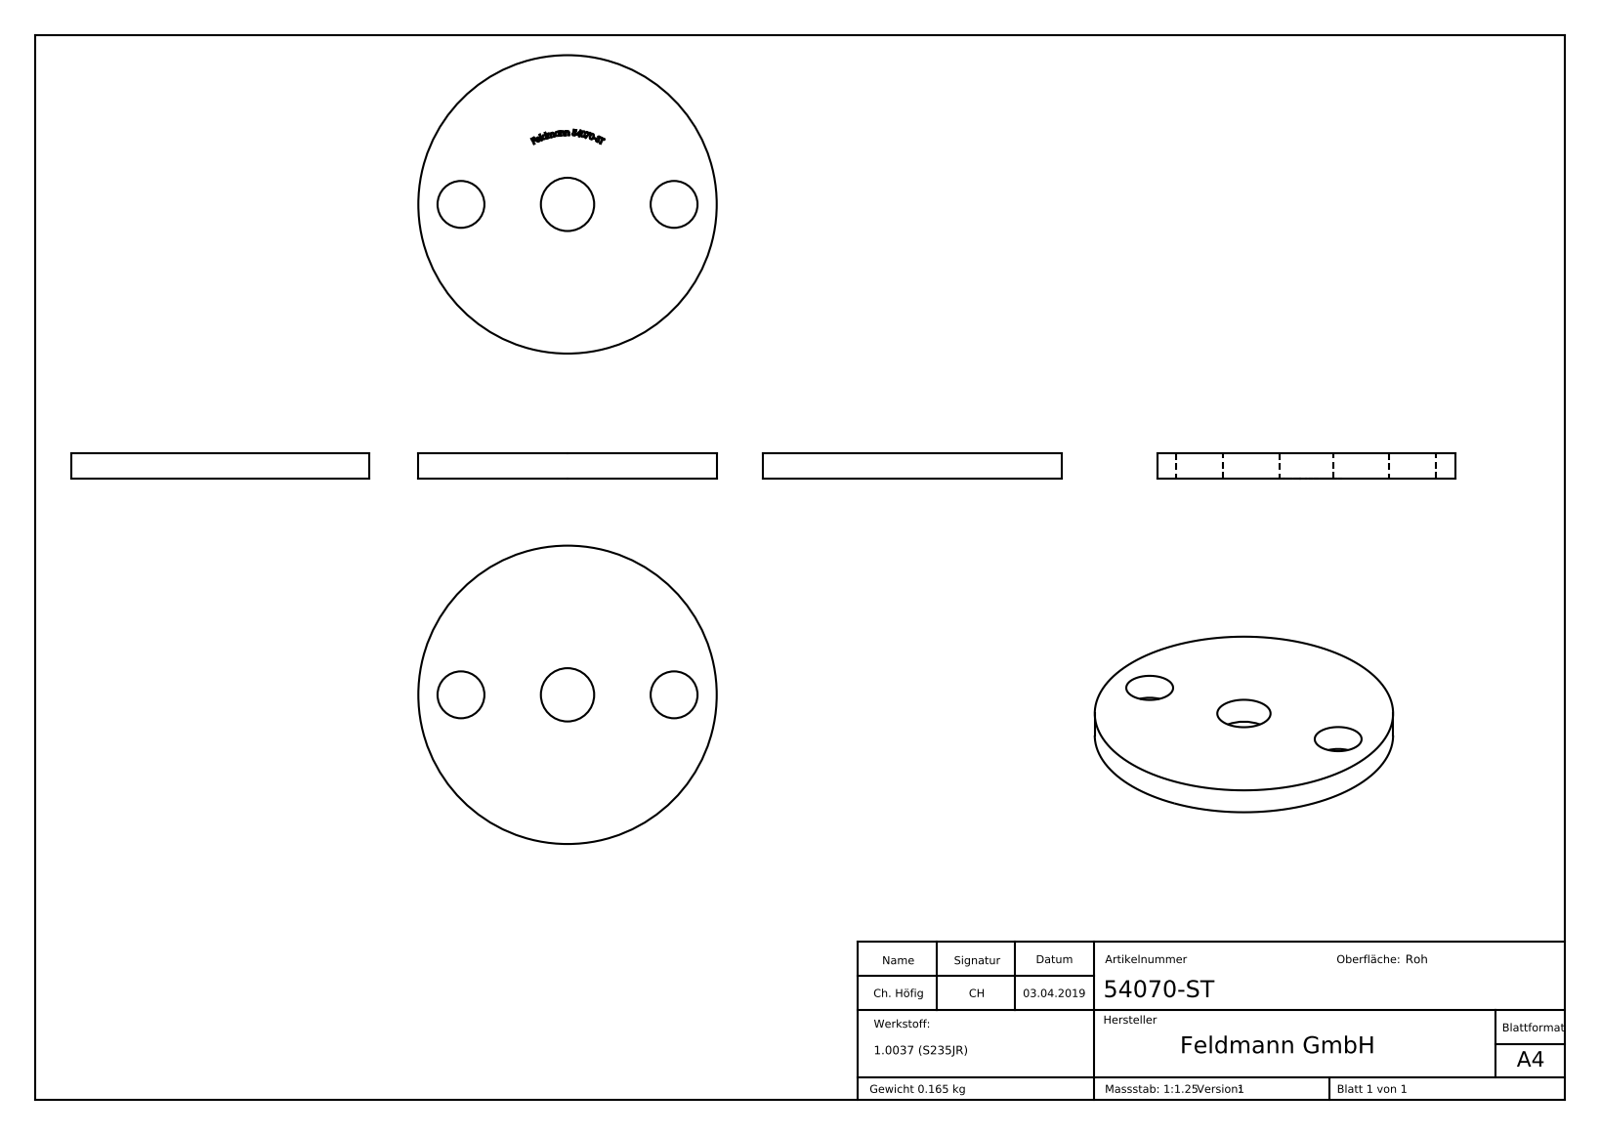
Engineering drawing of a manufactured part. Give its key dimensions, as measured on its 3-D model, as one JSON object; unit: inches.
{"part_name": "54070-ST", "step_written_by": "SolidWorks 2015 (CONFIG_CONTROL_DESIGN)", "units": "inches", "bodies": {"solids": 1, "faces": 214, "planar": 117, "cylindrical": 8, "other": 89}, "overall_size": [2.756, 2.756, 0.236], "volume_in3": 1.294, "surface_area_in2": 14.03, "round_holes": [[0.433, 2], [0.492, 1]], "round_bosses_or_shafts": [[2.756, 1]], "face_to_face_distances": [0.236, 0.232, 0.021, 0.026, 0.026, 0.033, 0.028, 0.031, 0.052, 0.029], "hole_center_spacings": [0.984, 1.969]}
